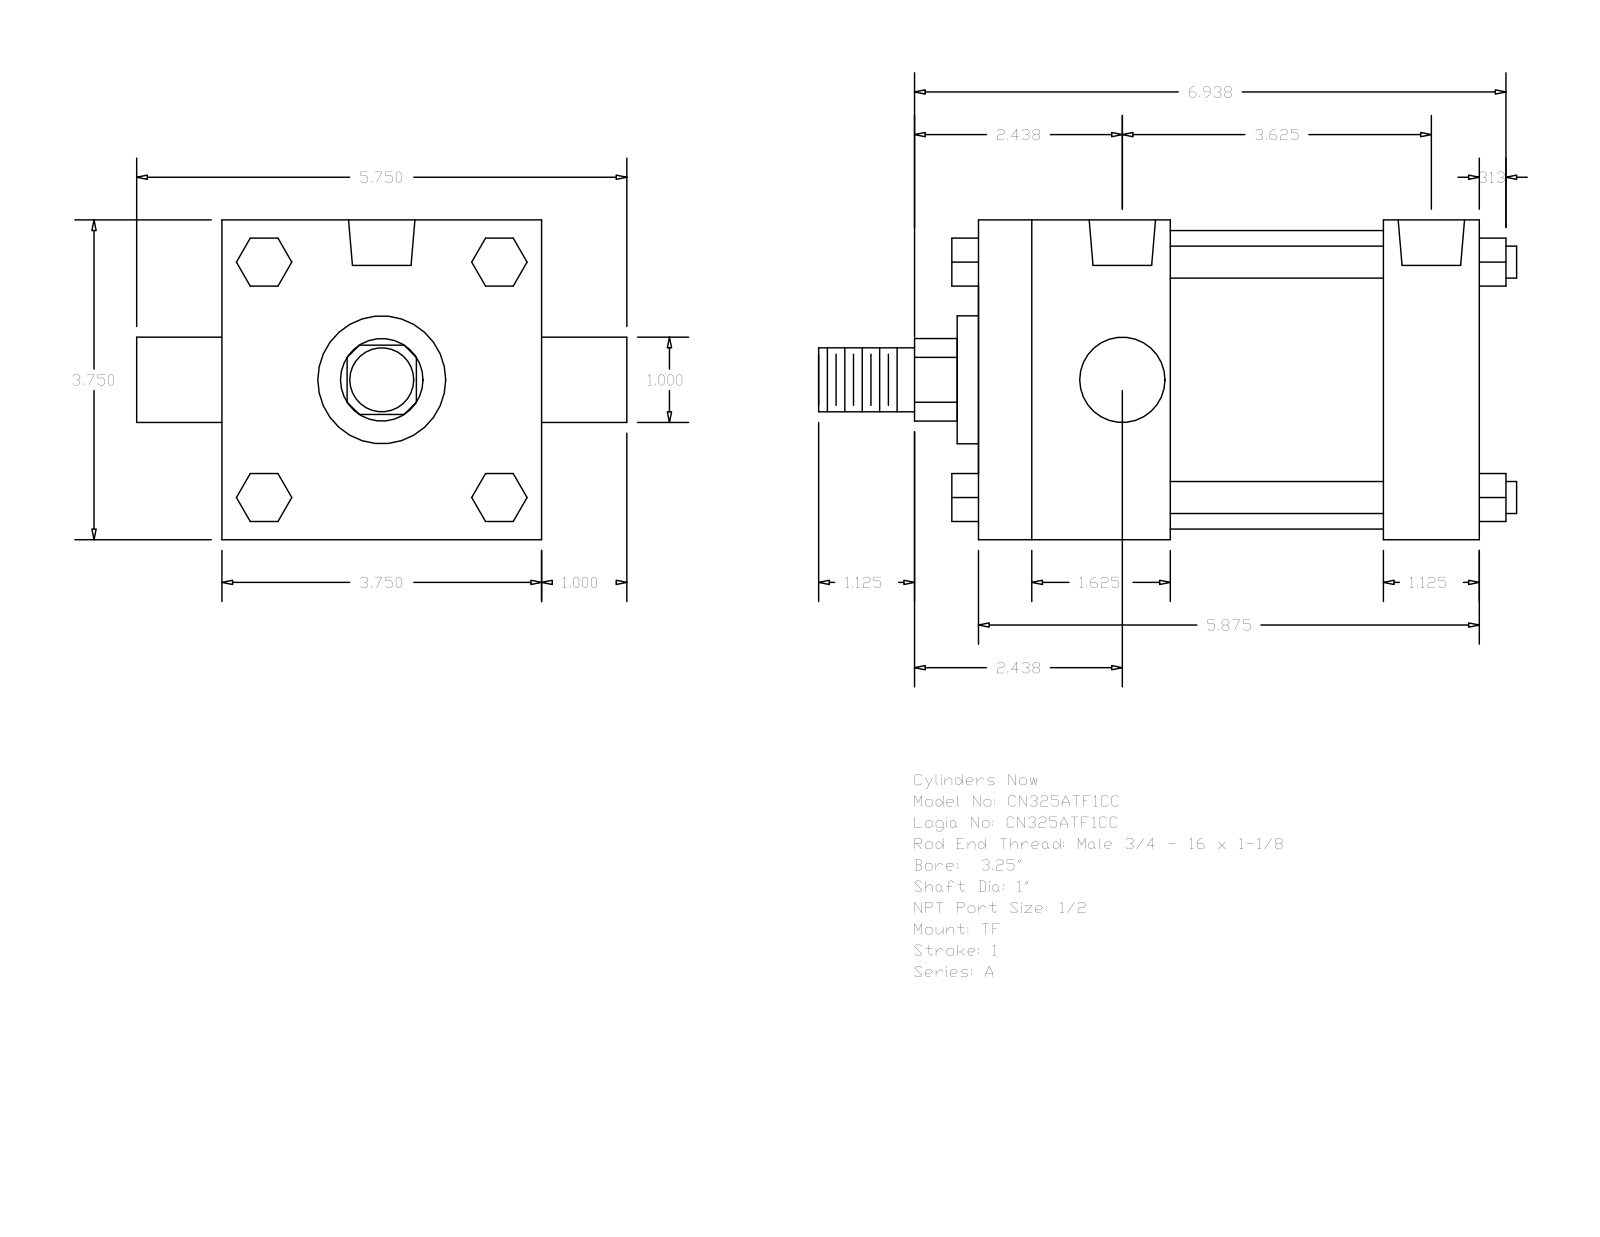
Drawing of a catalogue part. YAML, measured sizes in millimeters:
part_name: "A_TF__0325_1"
step_written_by: "GSSL Pune (CONFIG_CONTROL_DESIGN)"
units: millimeters
bodies: {solids: 0, faces: 120, planar: 92, cylindrical: 28, other: 0}
overall_size: [207.96, 146.05, 95.25]
round_holes:
  - {diameter: 8.73, count: 3}
  - {diameter: 19.77, count: 2}
round_bosses_or_shafts:
  - {diameter: 9.53, count: 4}
  - {diameter: 25.4, count: 2}
  - {diameter: 88.9, count: 1}
  - {diameter: 38.1, count: 1}
  - {diameter: 19.05, count: 1}
partial_cylinders:
  - {radius: 12.29, count: 1}
face_to_face_distances: [95.24, 149.23, 120.65, 63.5, 57.15, 92.08, 28.58, 14.28, 35.05, 60.71]
hole_center_spacings: [3.18, 88.9, 85.72, 92.08]
